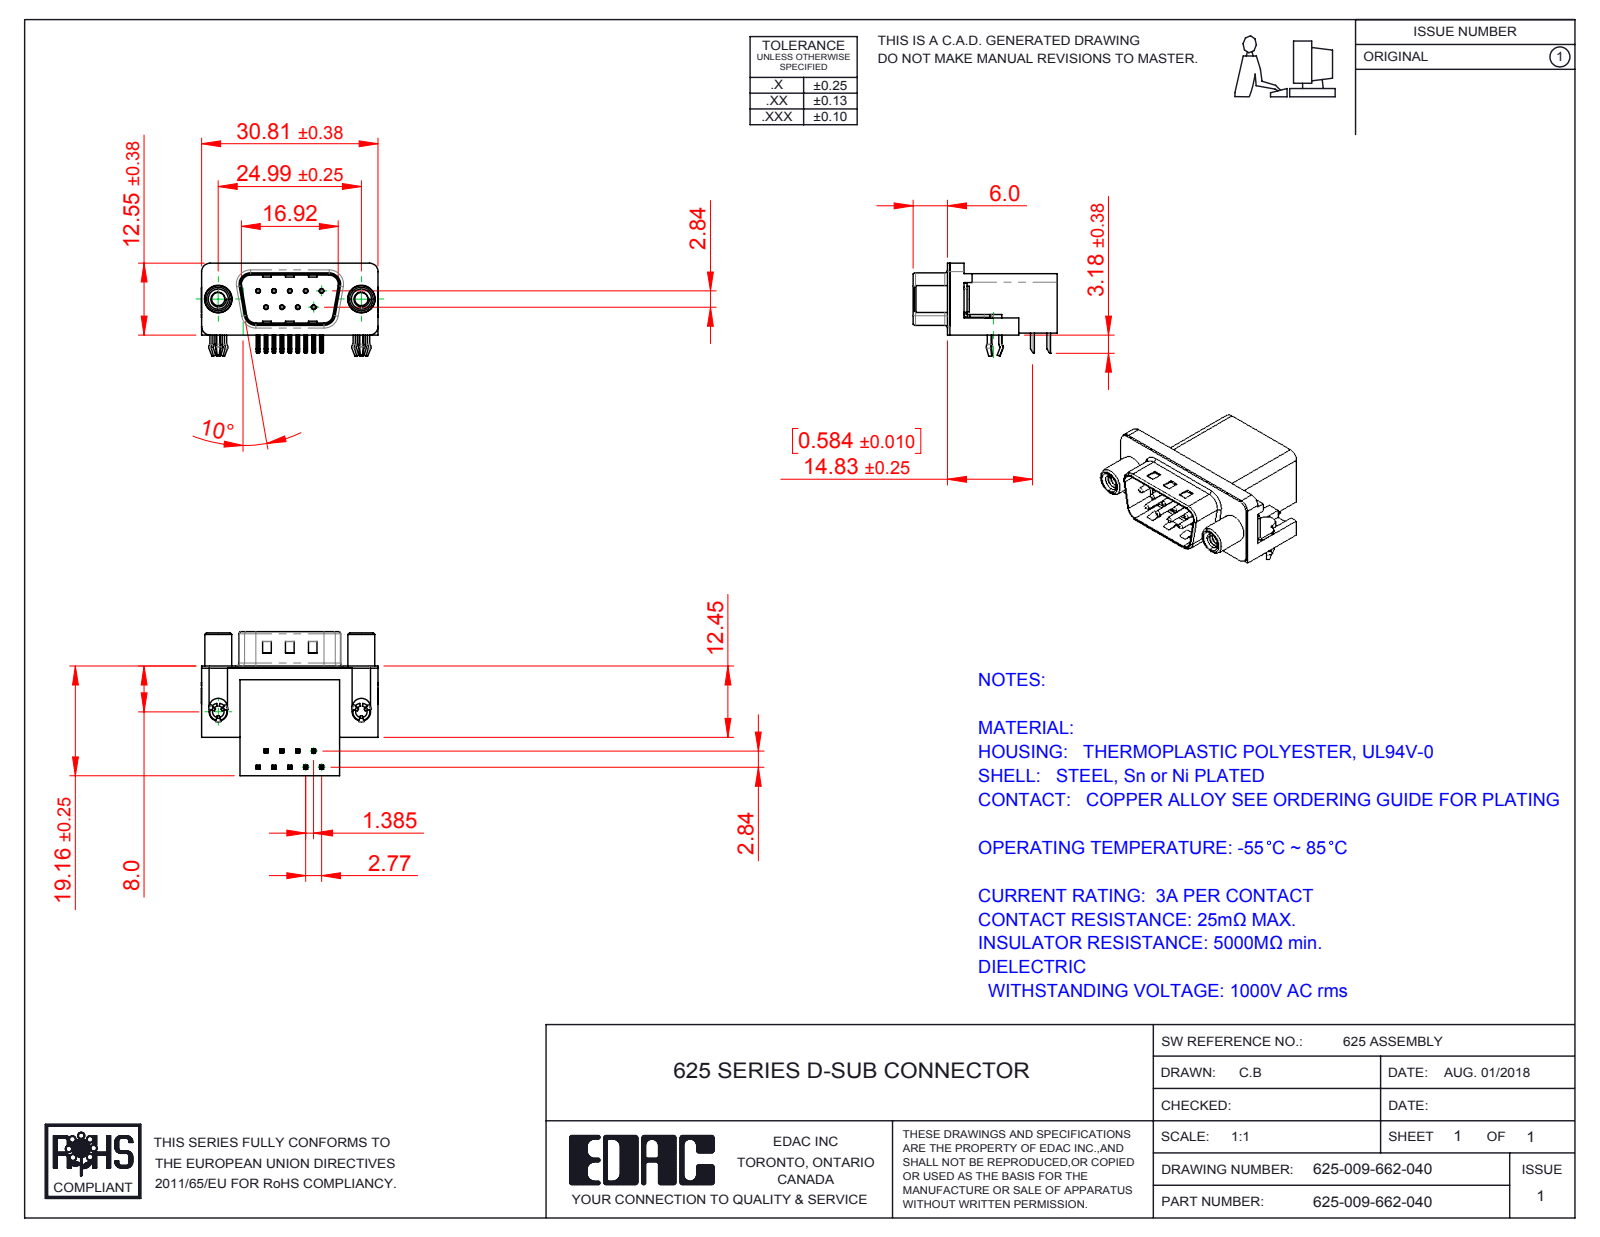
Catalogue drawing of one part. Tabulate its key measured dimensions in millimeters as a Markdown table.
| quantity | value |
| --- | --- |
| part name | 625 Contact Top; 625 Shell_9 Socket; 625 Contact Bottom; 625 Housing_9 Socket (+3 more) |
| STEP written by | SolidWorks 2016 (CONFIG_CONTROL_DESIGN) |
| units | millimeters |
| bodies | 15 solids, 1091 faces (603 planar, 331 cylindrical, 157 other) |
| overall size | 30.89 × 25.16 × 16.25 |
| volume | 4 574 mm³ |
| surface area | 5 211 mm² |
| round holes (diameter × count) | 0.35 × 9, 0.8 × 9, 2 × 2, 2.3 × 2, 3.1 × 2, 4 × 2, 4.8 × 2, 5 × 2 |
| round bosses / shafts (diameter × count) | 0.75 × 9, 4.9 × 2, 4.7 × 2, 4.5 × 2, 3.85 × 2, 3 × 2 |
| partial cylindrical surfaces (radius × count) | 0.25 × 40, 0.12 × 18, 1 × 16, 0.5 × 9, 1.5 × 8, 1.6 × 8, 0.9 × 4, 2 × 4 |
| main face-to-face distances | 0.4, 10.34, 18.76, 19.16, 16.26, 2.5, 2.9, 0.35, 10.69, 6.7 |
| hole center spacings | 3.16, 2.77, 5.54, 5.03, 5.04, 8.31, 7.48, 7.49 |
